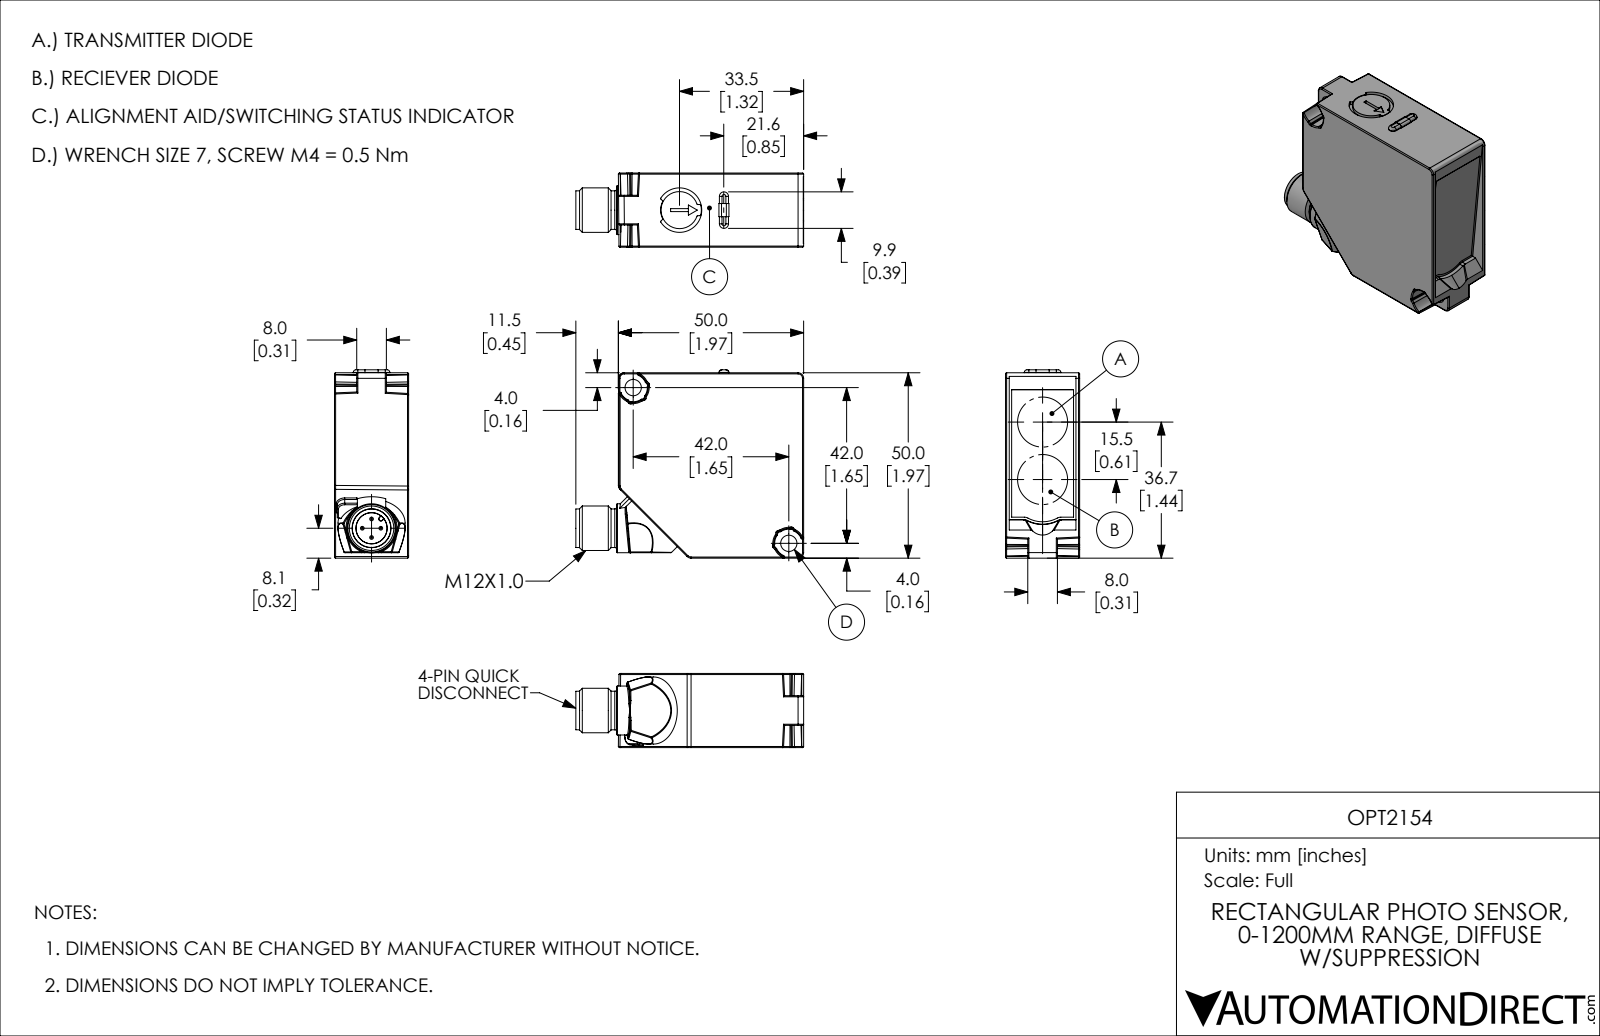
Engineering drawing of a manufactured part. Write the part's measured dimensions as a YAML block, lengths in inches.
part_name: "OPT2154"
step_written_by: "SolidWorks 2019 (AUTOMOTIVE_DESIGN)"
units: inches
bodies: {solids: 1, faces: 342, planar: 109, cylindrical: 120, other: 113}
overall_size: [2.42, 2, 0.787]
volume: 2.813
surface_area: 15.65
round_holes:
  - {diameter: 0.173, count: 2}
  - {diameter: 0.472, count: 1}
  - {diameter: 0.713, count: 1}
round_bosses_or_shafts:
  - {diameter: 0.039, count: 4}
  - {diameter: 0.52, count: 1}
  - {diameter: 0.472, count: 1}
  - {diameter: 0.409, count: 1}
  - {diameter: 0.394, count: 1}
partial_cylinders:
  - {radius: 0.012, count: 64}
  - {radius: 0.008, count: 8}
  - {radius: 0.059, count: 5}
  - {radius: 0.079, count: 5}
  - {radius: 0.028, count: 4}
  - {radius: 0.048, count: 2}
  - {radius: 0.201, count: 1}
  - {radius: 0.232, count: 1}
face_to_face_distances: [0.787, 1.969, 0.039, 0.748, 0.236, 0.551, 0.197, 0.512, 0.058, 1.911]
hole_center_spacings: [2.339]
